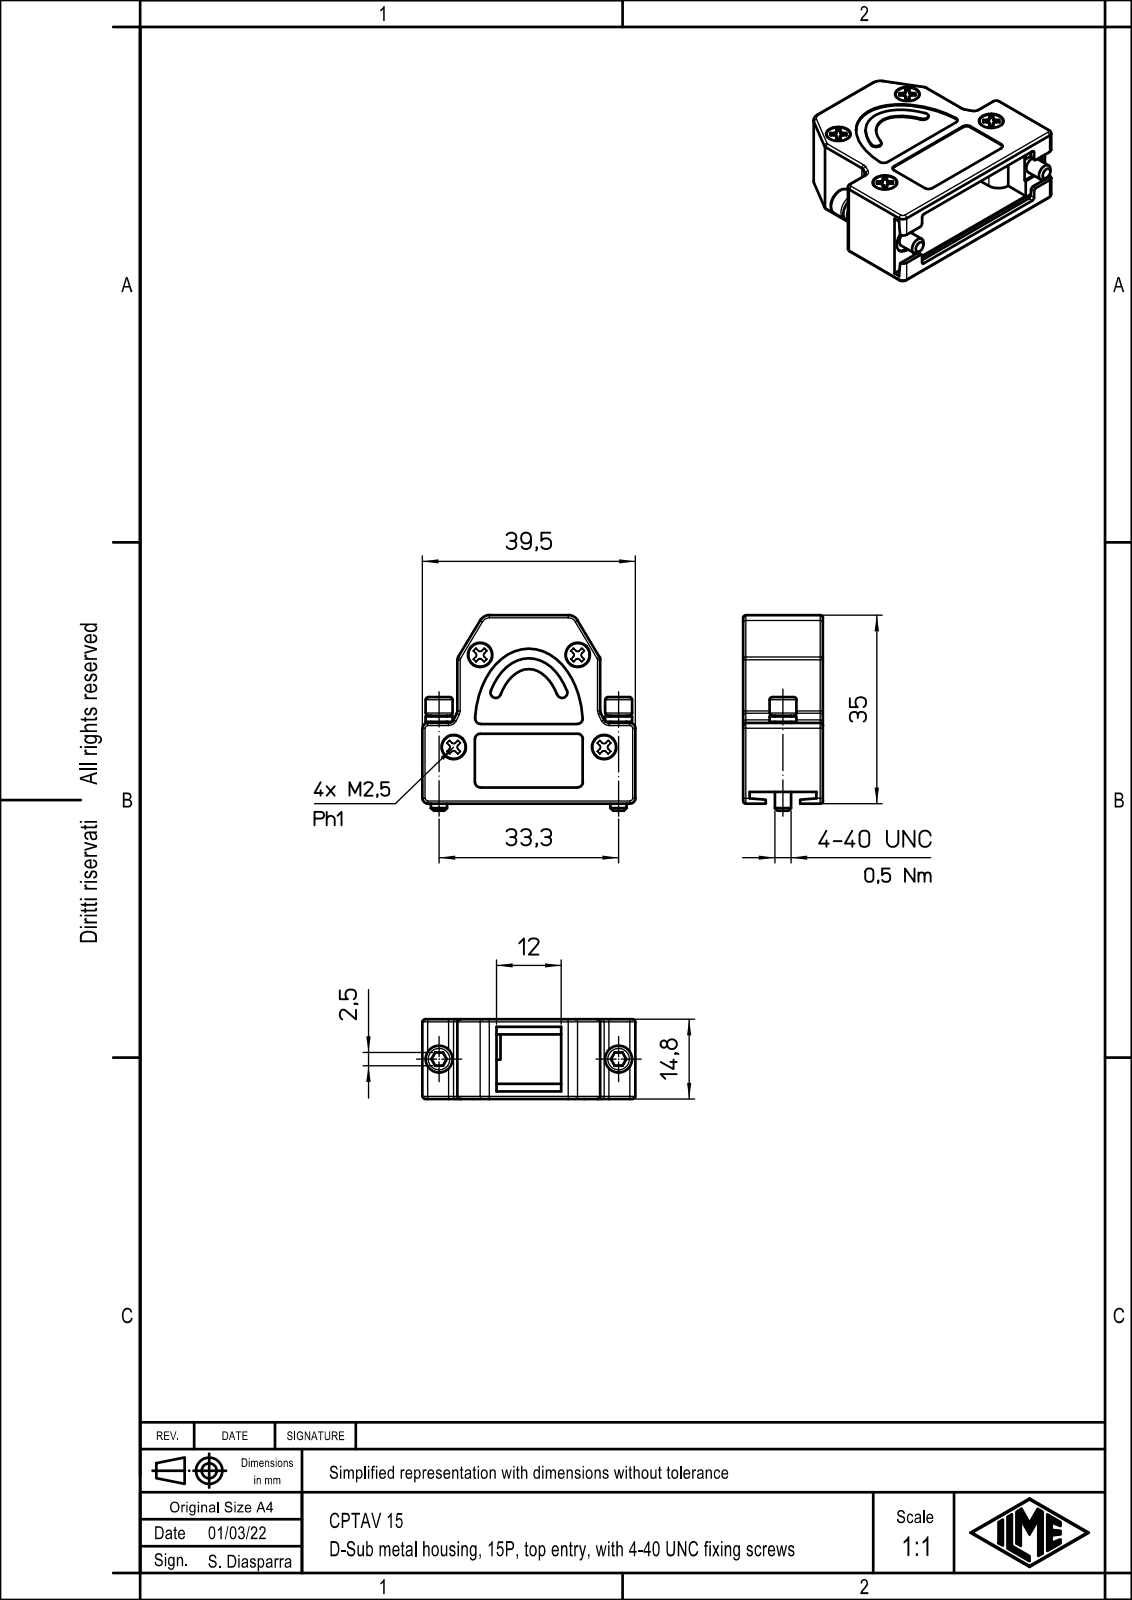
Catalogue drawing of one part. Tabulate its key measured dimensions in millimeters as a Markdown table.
| quantity | value |
| --- | --- |
| part name | CPTAV_15 |
| STEP written by | Creo Elements/Direct Modeling 20.1B 02-Apr-2019 (C) Parametric Technology GmbH (AUTOMOTIVE_DESIGN) |
| units | millimeters |
| bodies | 1 solid, 698 faces (147 planar, 205 cylindrical, 346 other) |
| overall size | 39.5 × 36.3 × 14.8 |
| volume | 7 010 mm³ |
| surface area | 6 879 mm² |
| round bosses / shafts (diameter × count) | 5 × 2, 3 × 2 |
| partial cylindrical surfaces (radius × count) | 0.5 × 46, 1 × 16, 2 × 3, 1.87 × 2, 2.55 × 2, 0.99 × 1, 0.99 × 1 |
| main face-to-face distances | 13.3, 1.5, 1.3, 13.1, 14.6, 11.8, 14.8, 14.4, 1.2, 6.5 |
